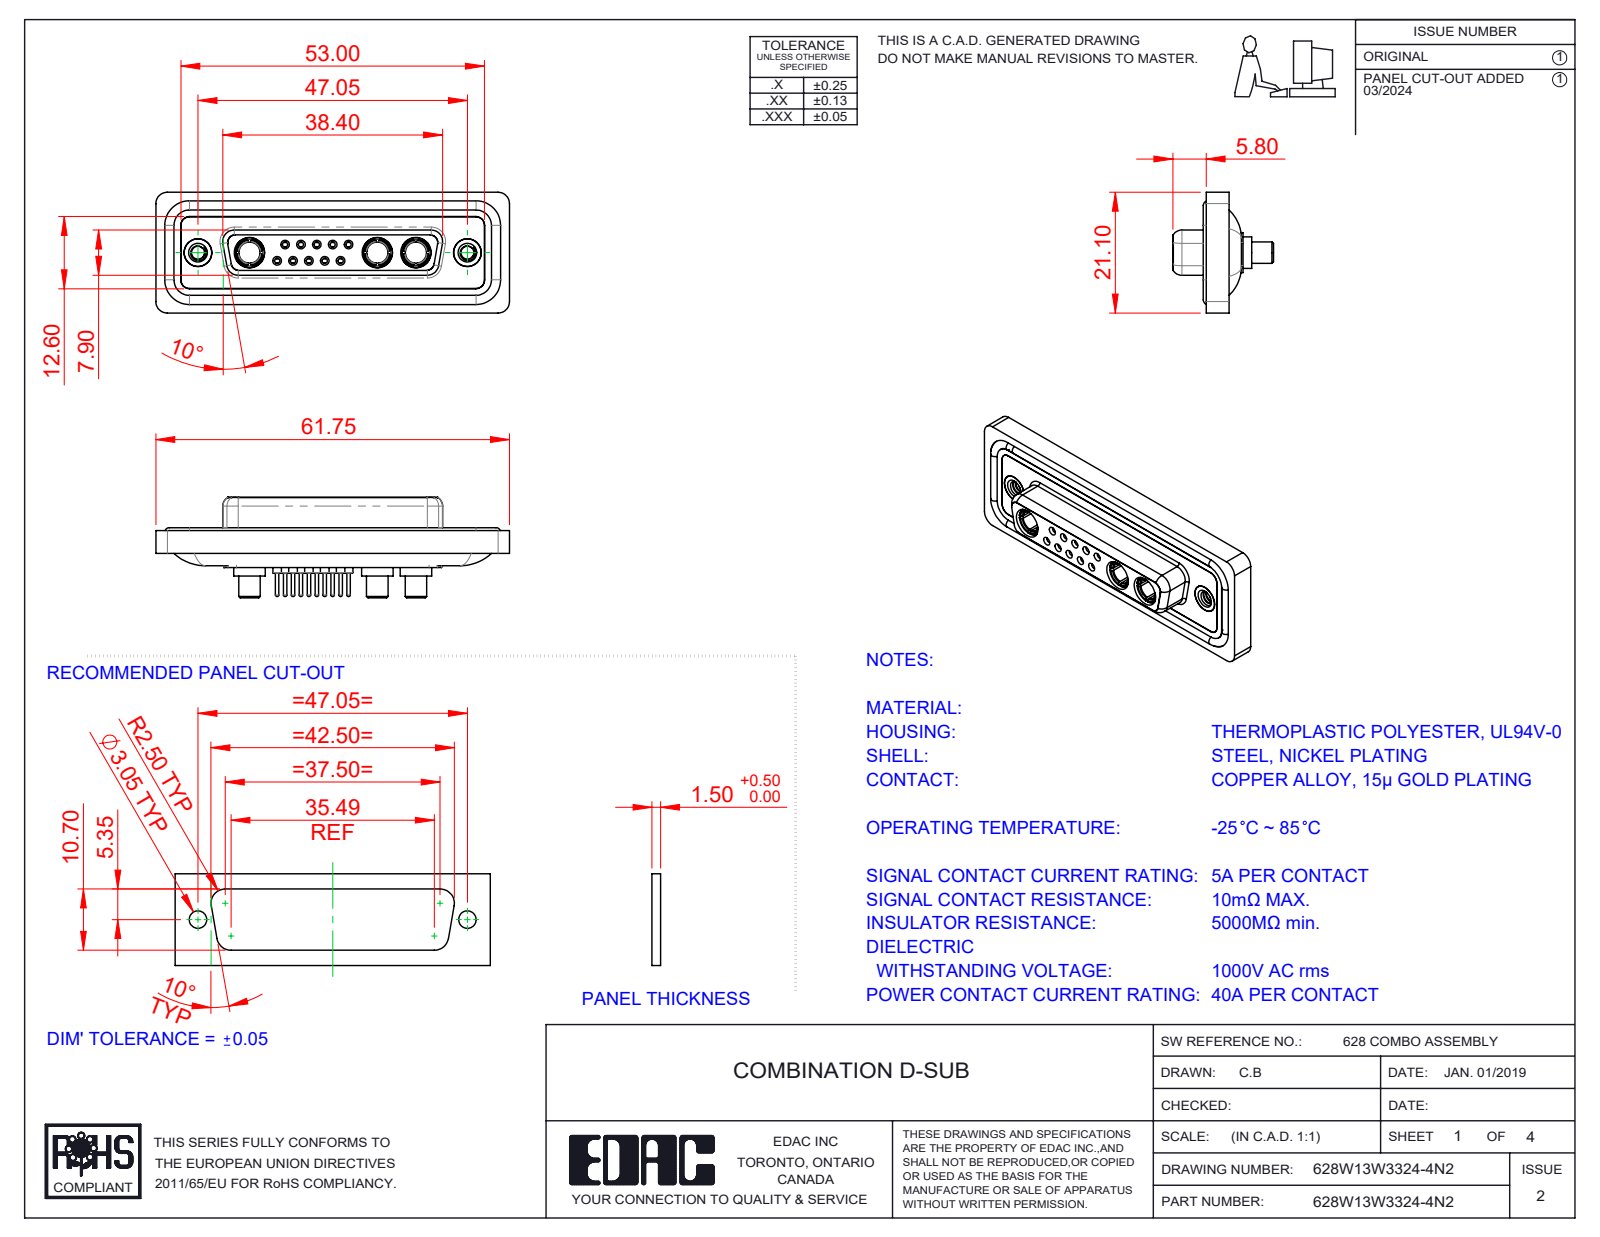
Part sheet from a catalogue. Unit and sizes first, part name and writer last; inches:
Units: inches
Overall size (bounding box): 2.431 × 0.831 × 0.691
Round holes (diameter × count): ⌀0.035 ×10, ⌀0.043 ×10, ⌀0.059 ×10, ⌀0.079 ×10, ⌀0.063 ×5, ⌀0.067 ×5, ⌀0.191 ×5, ⌀0.146 ×3, ⌀0.209 ×3, ⌀0.089 ×2, ⌀0.157 ×2, ⌀0.159 ×2
Round bosses / shafts (diameter × count): ⌀0.087 ×10, ⌀0.024 ×10, ⌀0.063 ×9, ⌀0.217 ×3, ⌀0.205 ×3, ⌀0.195 ×3, ⌀0.187 ×3, ⌀0.148 ×3
Partial cylindrical surfaces — rounded edges, fillets, slot ends (radius × count): R0.059 ×22, R0.079 ×18, R0.053 ×8, R0.063 ×8, R0.01 ×4, R0.02 ×4, R0.024 ×4, R0.026 ×4
Main face-to-face distances: 0.016, 0.071, 0.293, 0.222, 0.02, 0.26, 0.278, 0.063, 0.114, 0.043
Hole centre spacings: 0.124, 0.109, 0.198, 0.198, 0.218, 0.327, 0.295, 0.109
Volume: 0.508 in³ · Surface area: 21.3 in²
Bodies: 23 solids, 1158 faces (342 planar, 447 cylindrical, 369 other)
Part name (STEP PRODUCT): 628Combo Contact Row 1_24; 628Combo Waterproof Housing_25 Contacts; 628Combo Contact Row 2_24; 628Combo Shell Front_25 Contacts (+5 more)
STEP written by: SolidWorks 2023 (CONFIG_CONTROL_DESIGN)
